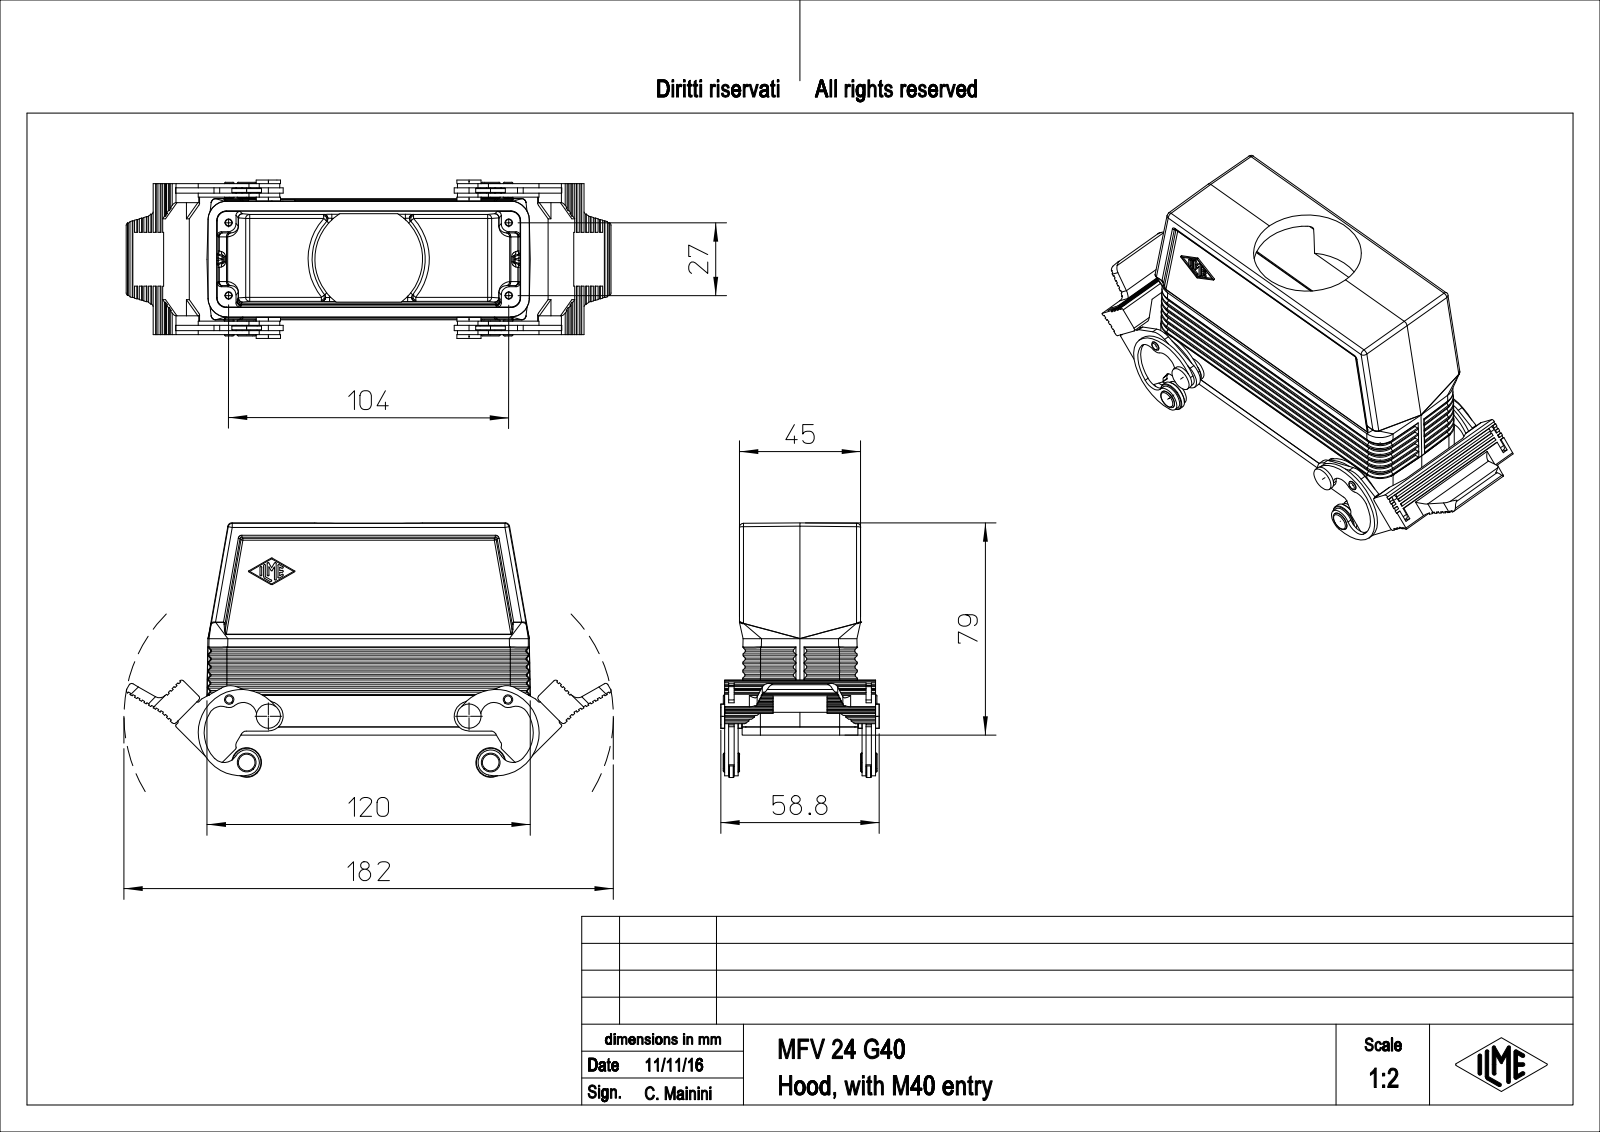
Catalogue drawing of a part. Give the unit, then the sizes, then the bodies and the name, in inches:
Units: inches
Overall size (bounding box): 7.085 × 3.719 × 2.315
Round holes (diameter × count): ⌀0.108 ×4, ⌀0.197 ×4, ⌀0.122 ×2, ⌀0.157 ×2, ⌀1.575 ×1
Round bosses / shafts (diameter × count): ⌀0.433 ×2, ⌀0.354 ×2, ⌀0.276 ×2, ⌀0.189 ×2, ⌀0.138 ×2, ⌀0.118 ×2
Partial cylindrical surfaces — rounded edges, fillets, slot ends (radius × count): R0.02 ×86, R0.059 ×16, R0.118 ×12, R0.039 ×10, R0.276 ×10, R0.197 ×6, R0.079 ×4, R0.138 ×4
Main face-to-face distances: 0.079, 0.039, 1.693, 0.138, 2.008, 0.157, 0.059, 0.236, 0.276, 2.067
Hole centre spacings: 0.748, 0.752, 0.955, 1.063, 1.341, 2.115, 2.115, 3.929
Volume: 8.401 in³ · Surface area: 117.3 in²
Bodies: 1 solid, 1267 faces (675 planar, 408 cylindrical, 184 other)
Part name (STEP PRODUCT): MFV_24_G40
STEP written by: PTC Creo Elements/Direct Modeling 19.0E 27-Jun-2016 (C) Parametric Technology GmbH (AUTOMOTIVE_DESIGN)
